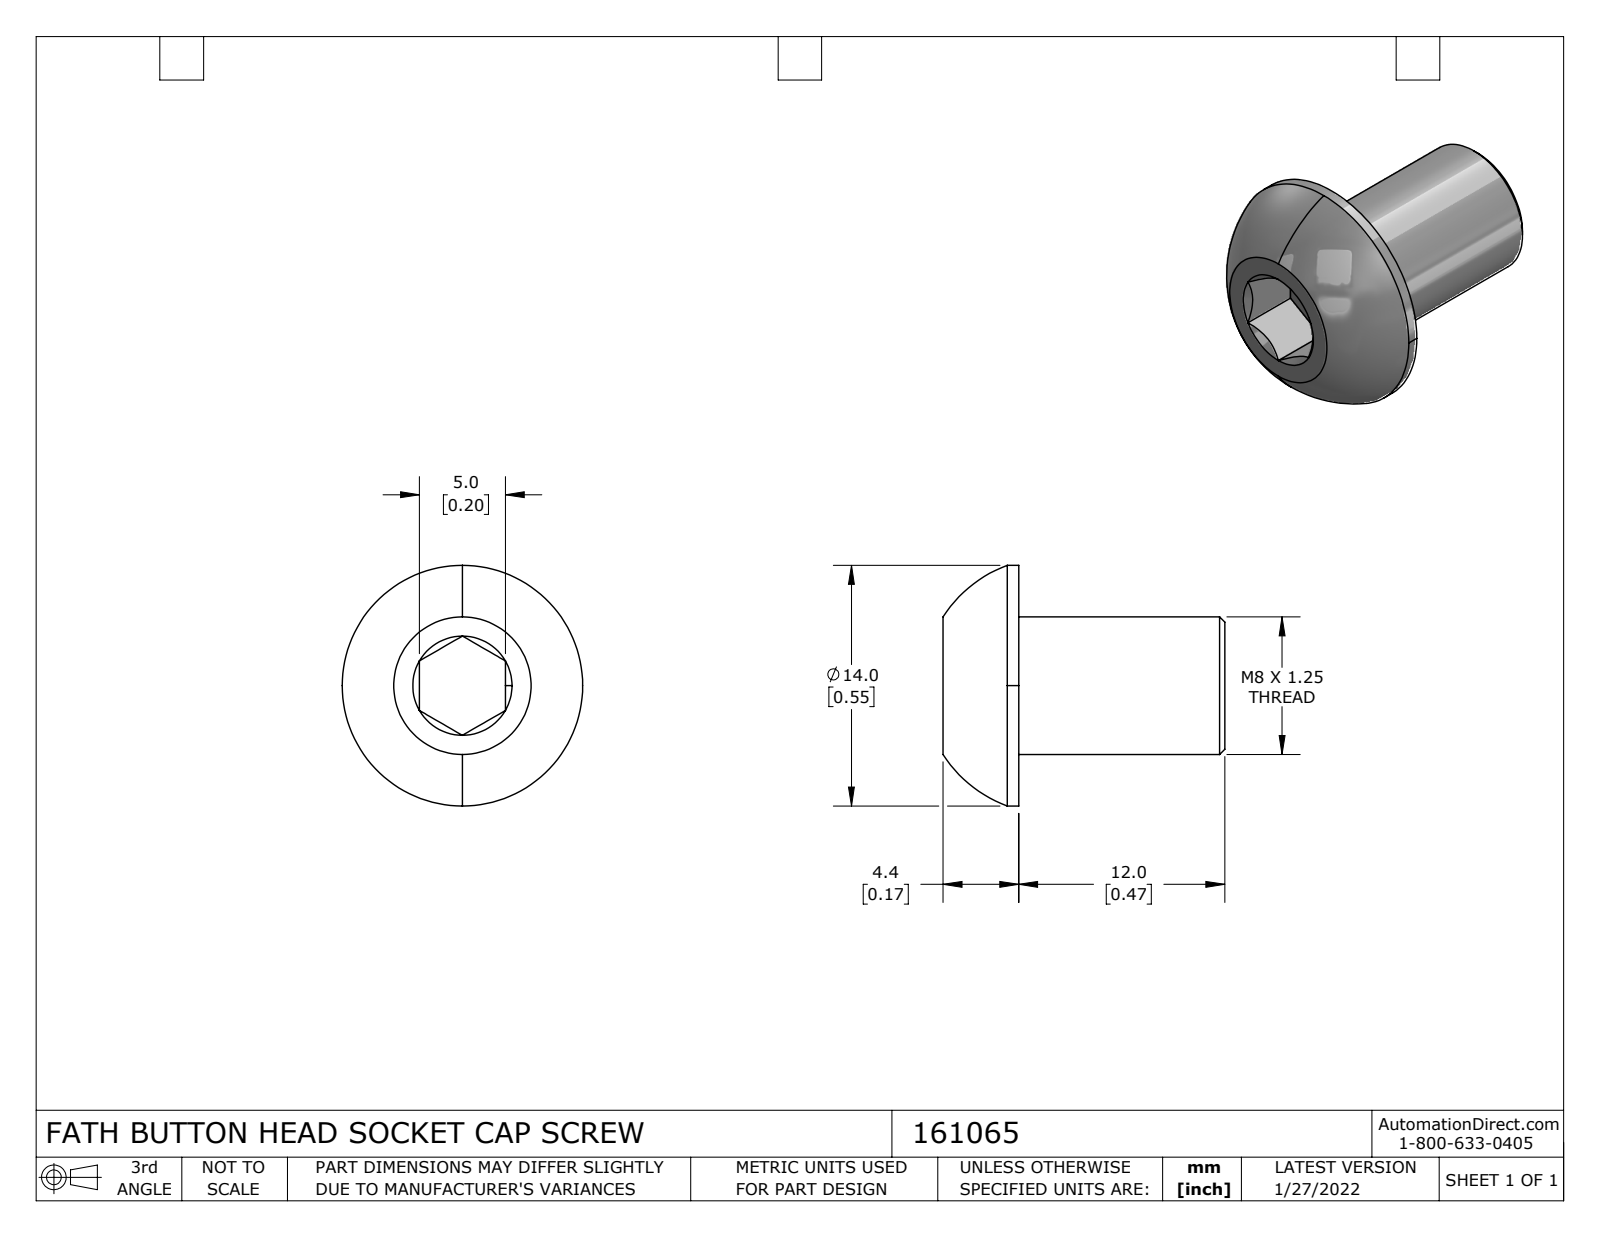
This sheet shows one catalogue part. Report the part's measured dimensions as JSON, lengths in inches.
{"part_name": "161065", "step_written_by": "SolidWorks 2021 (CONFIG_CONTROL_DESIGN)", "units": "inches", "bodies": {"solids": 1, "faces": 25, "planar": 10, "cylindrical": 4, "other": 11}, "overall_size": [0.646, 0.551, 0.551], "volume_in3": 0.063, "surface_area_in2": 1.18, "round_bosses_or_shafts": [[0.551, 1], [0.315, 1]], "face_to_face_distances": [0.472, 0.197, 0.646, 0.173, 0.508, 0.035, 0.138]}
